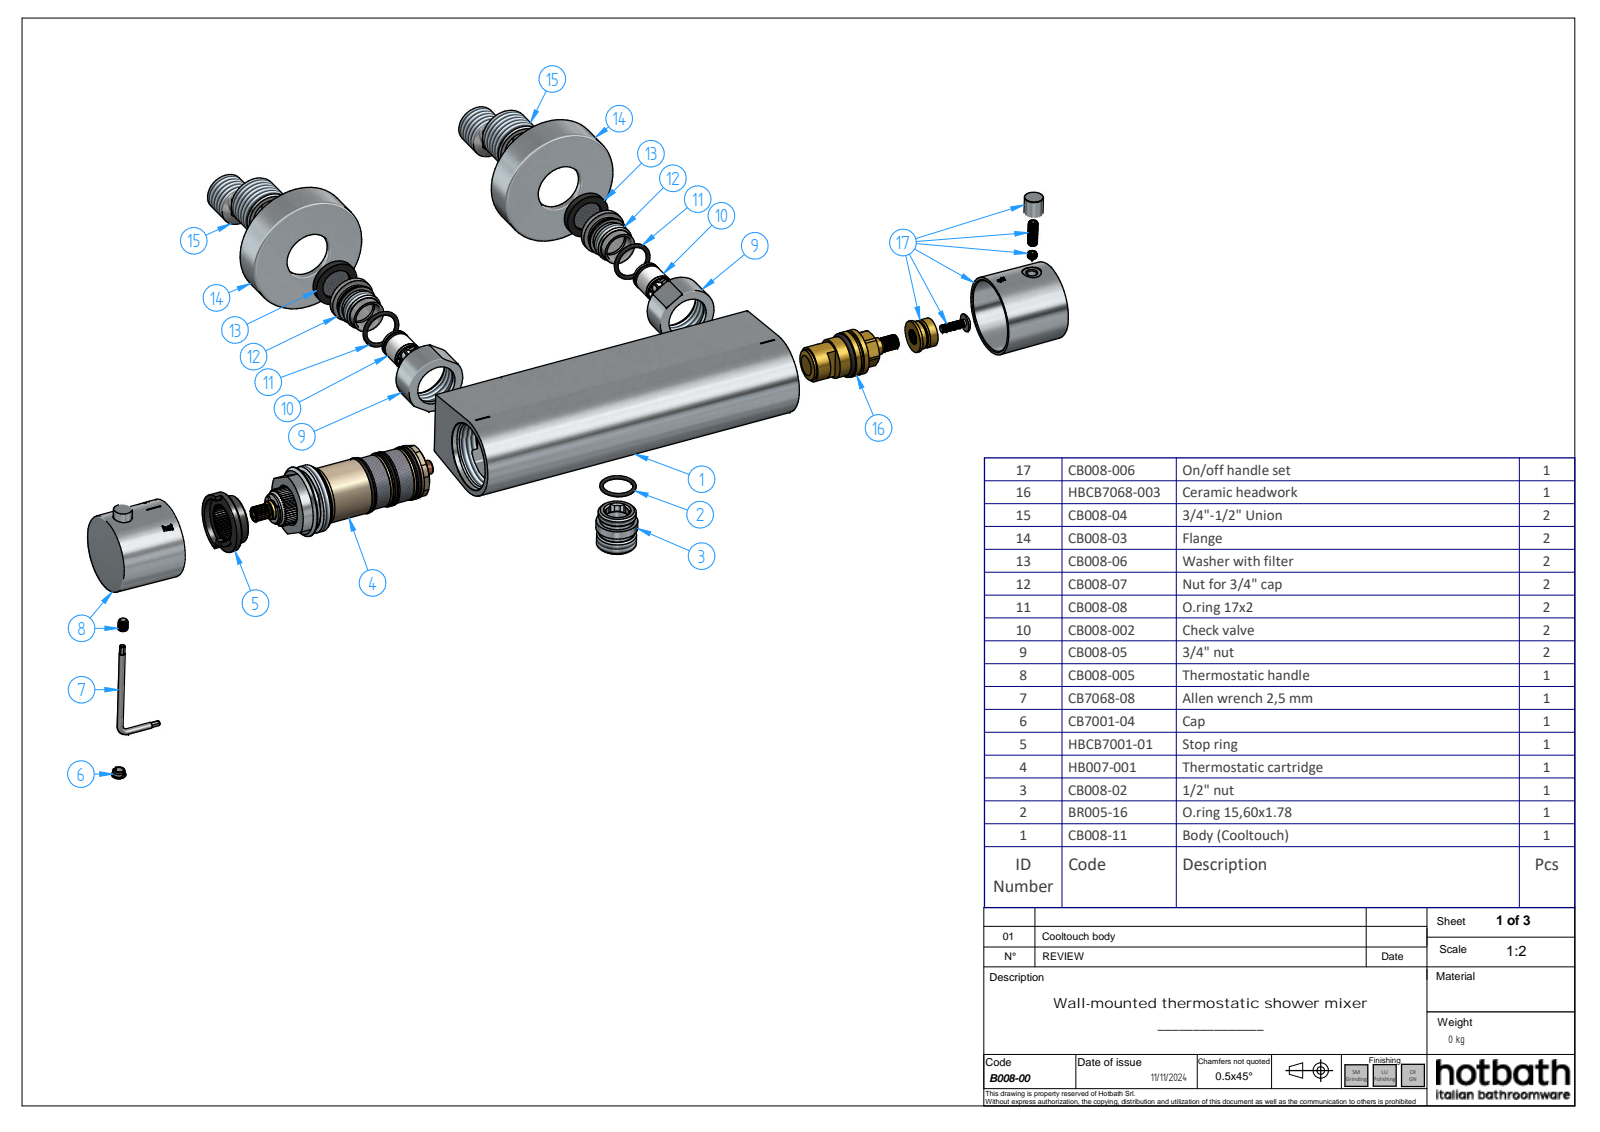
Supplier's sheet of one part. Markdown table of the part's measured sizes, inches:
| quantity | value |
| --- | --- |
| part name | B008-00 Rel1; CB008-006_oa_0; CB008-13; CB7068-04 (+8 more) |
| STEP written by | Solid Edge (AUTOMOTIVE_DESIGN) |
| units | inches |
| bodies | 13 solids, 1120 faces (409 planar, 303 cylindrical, 408 other) |
| overall size | 10.211 × 3.661 × 2.579 |
| volume | 14.22 in³ |
| surface area | 232.7 in² |
| round holes (diameter × count) | 0.402 × 3, 0.593 × 3, 0.728 × 3, 0.118 × 2, 0.138 × 2, 0.163 × 2, 0.205 × 2, 0.622 × 2, 0.827 × 2, 0.874 × 2, 0.95 × 2, 0.984 × 2 |
| round bosses / shafts (diameter × count) | 0.787 × 3, 2.52 × 2, 0.945 × 2, 0.854 × 2, 0.756 × 2, 0.711 × 2, 0.697 × 2, 0.394 × 2 |
| partial cylindrical surfaces (radius × count) | 0.079 × 118, 0.02 × 7, 0.008 × 6, 0.118 × 4, 0.244 × 3, 0.078 × 2, 0.083 × 2, 0.138 × 2 |
| main face-to-face distances | 0.157, 0.02, 0.138, 0.709, 0.807, 0.669, 0.65, 0.827, 0.689, 0.039 |
| hole center spacings | 0.079, 0.359, 0.468, 0.469, 0.587, 0.976, 1.055, 4.641 |
